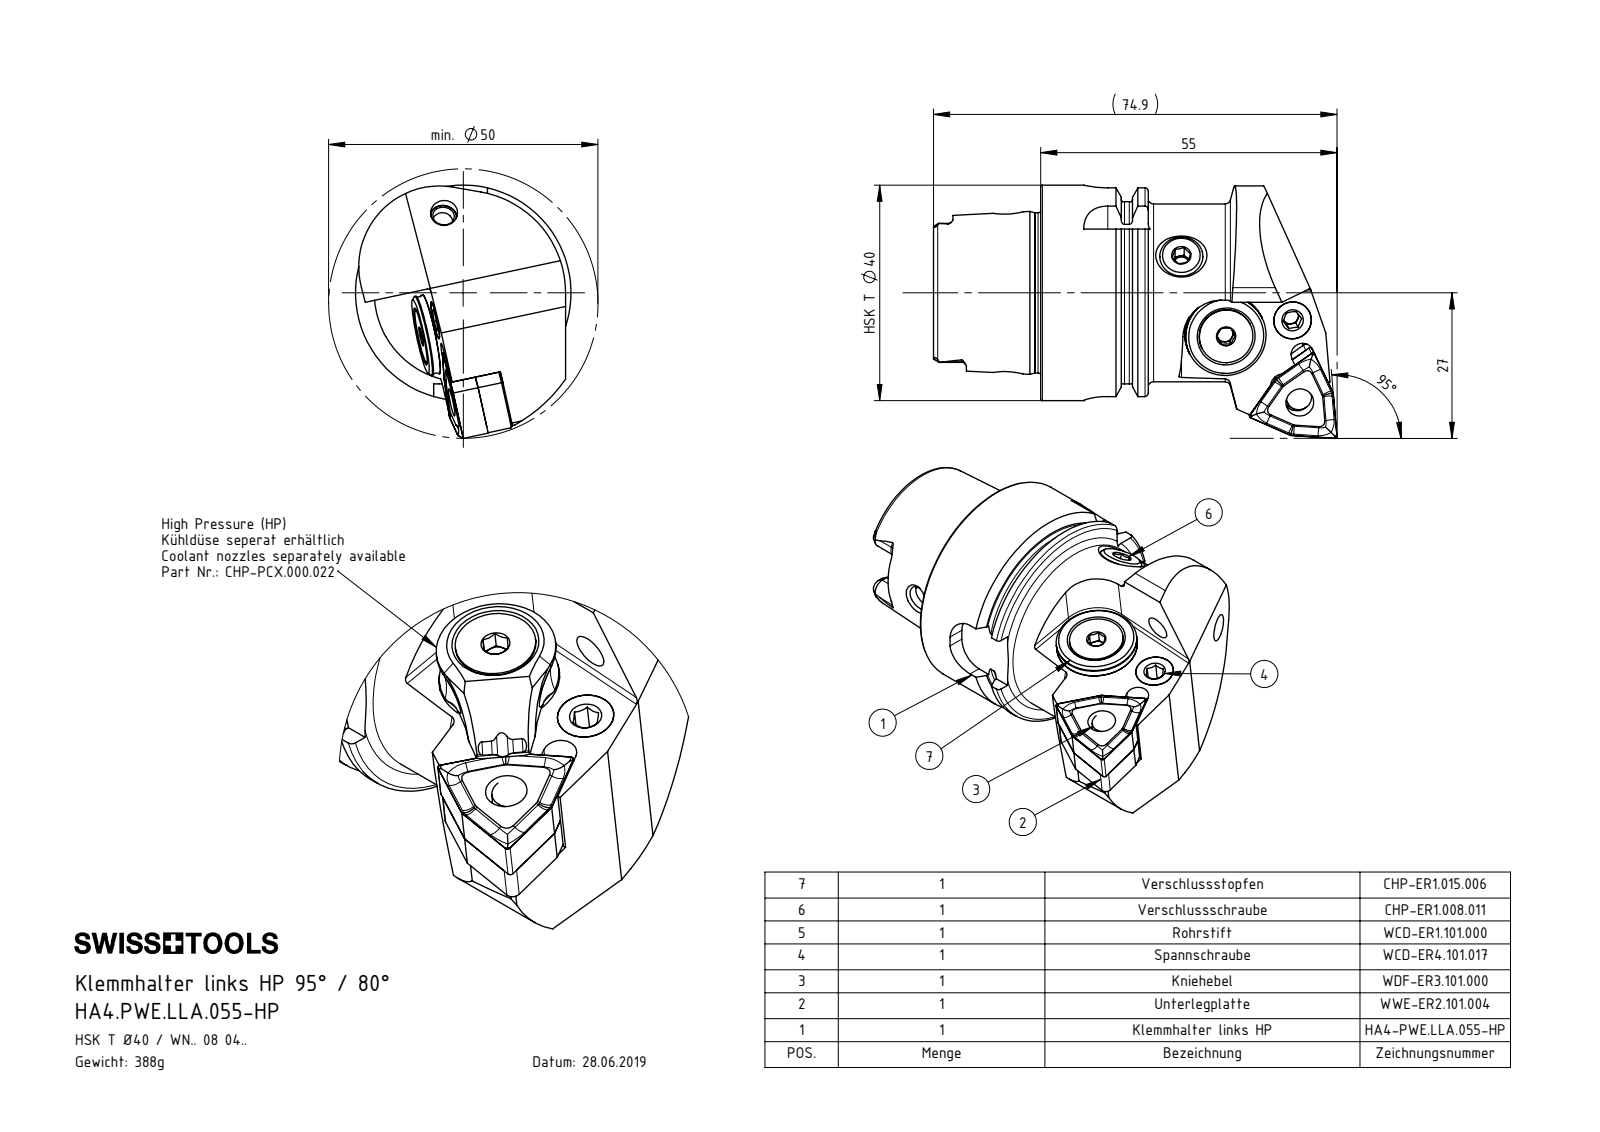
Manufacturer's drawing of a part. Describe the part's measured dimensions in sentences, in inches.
The part is named "WDF-ER3.101.000_A; CHP-ER1.015.006_A; HA4-PWE.LLA.055-HP_D; CHP-ER1.008.011_A (+8 more)". Its 3-D file was written by "SolidWorks 2017 (AUTOMOTIVE_DESIGN)". It is 15 solids with 603 faces: 175 planar, 166 cylindrical and 262 other. Overall it measures 2.949 by 1.85 by 1.575 inches. Its volume is 3 cubic inches and its surface area 32.03 square inches. Round holes: 6 of diameter 0.165, 3 of diameter 0.197, 2 of diameter 0.157, 2 of diameter 0.276, 1 of diameter 0.047, 1 of diameter 0.079, 1 of diameter 0.098, 1 of diameter 0.118, 1 of diameter 0.181, 1 of diameter 0.203, 1 of diameter 0.205, 1 of diameter 0.264. Round bosses or shafts: 3 of diameter 0.197, 2 of diameter 0.315, 1 of diameter 1.575, 1 of diameter 1.368, 1 of diameter 1.299, 1 of diameter 1.17, 1 of diameter 0.591, 1 of diameter 0.528. Partial cylindrical surfaces (rounded edges, fillets, slot ends): 6 of radius 0.035, 4 of radius 0.074, 4 of radius 0.098, 4 of radius 0.177, 3 of radius 0.016, 3 of radius 0.039, 2 of radius 0.02, 1 of radius 0.083. The main face-to-face distances are 0.187, 0.177, 0.176, 0.186, 0.363, 0.313, 0.785, 0.472, 0.783, 1.096. The hole center spacings are 0.626, 0.755, 0.176, 0.176, 0.177, 0.177, 0.337, 0.338.
